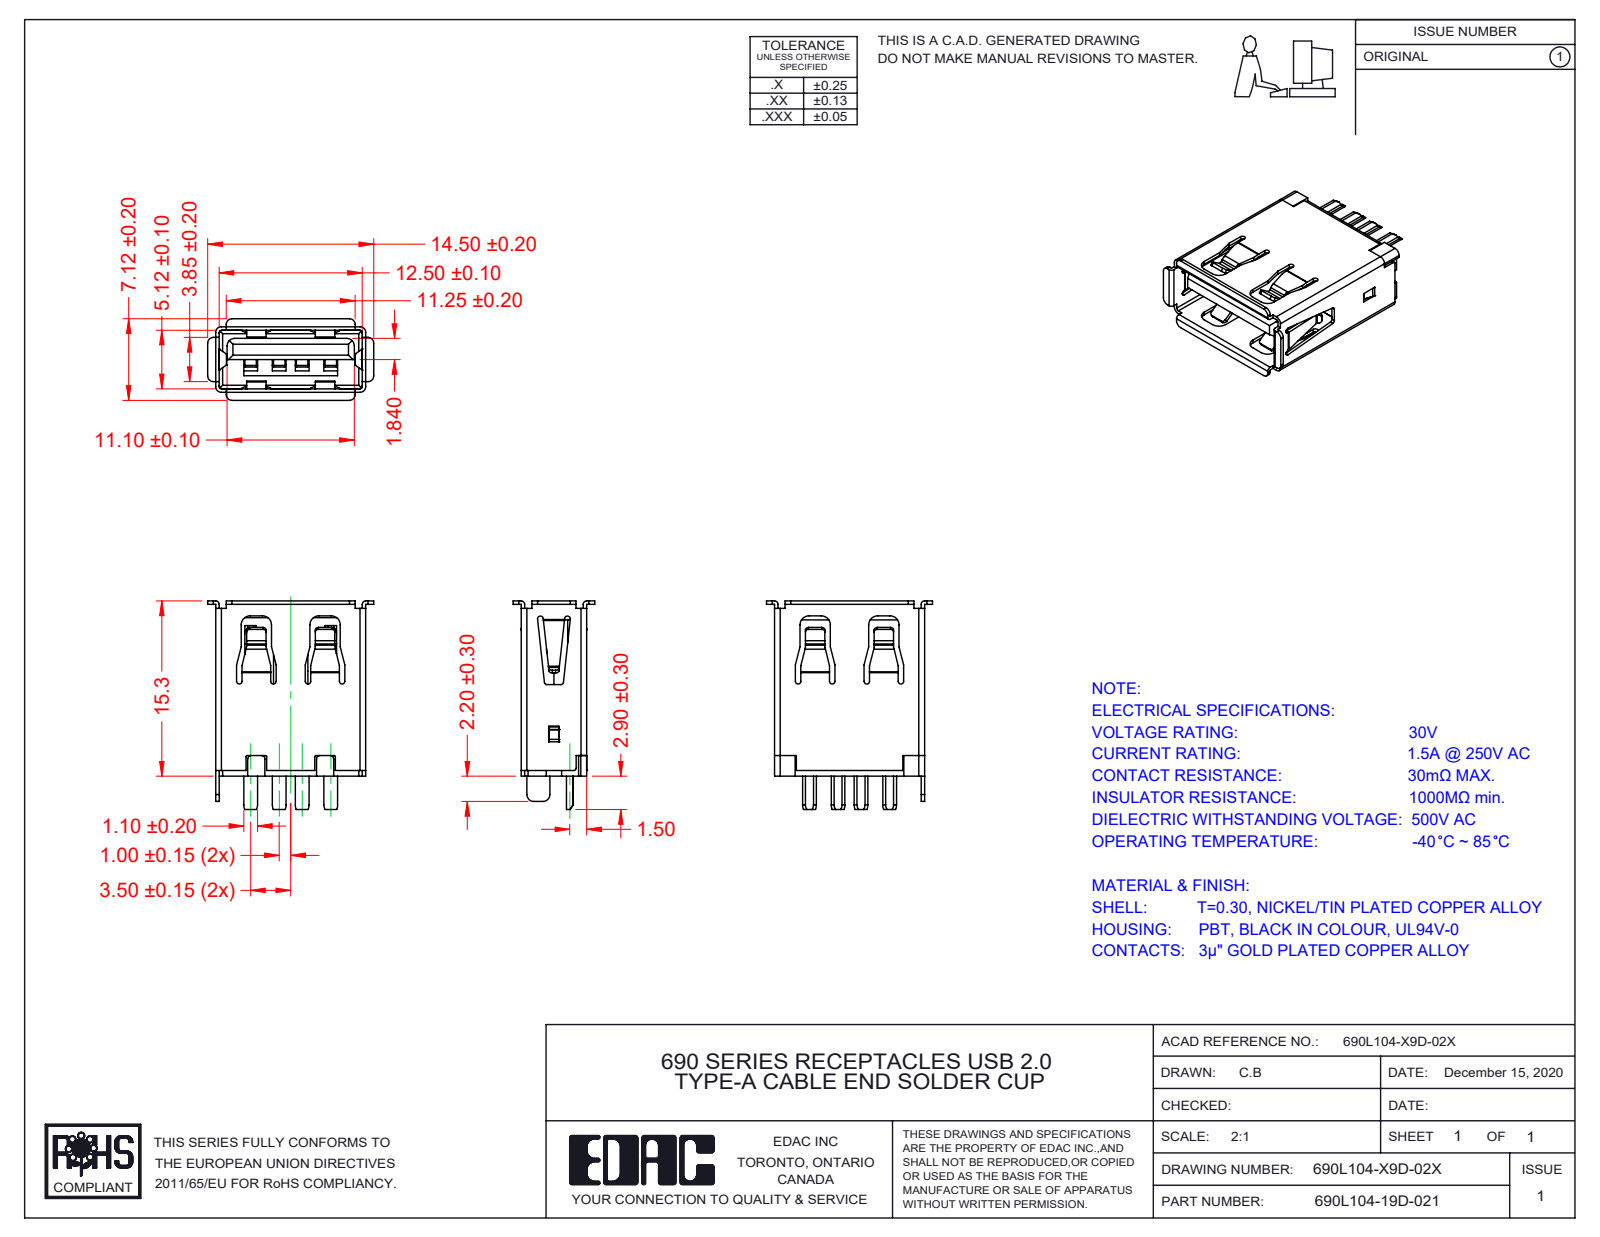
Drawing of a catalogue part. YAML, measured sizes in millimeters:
part_name: "690L104-19D-021; Shell 690L104-X9D-02X; Insulator 690L104-X9D-02X_Black; Insulator 2 690L104-X9D-02X_Black (+1 more)"
step_written_by: "SolidWorks 2020 (AUTOMOTIVE_DESIGN)"
units: millimeters
bodies: {solids: 7, faces: 790, planar: 558, cylindrical: 184, other: 48}
overall_size: [18.2, 14.5, 7.12]
volume: 618
surface_area: 2270
partial_cylinders:
  - {radius: 0.3, count: 19}
  - {radius: 0.5, count: 19}
  - {radius: 0.1, count: 16}
  - {radius: 0.2, count: 12}
  - {radius: 0.6, count: 9}
  - {radius: 0.27, count: 8}
  - {radius: 0.25, count: 6}
  - {radius: 0.4, count: 6}
face_to_face_distances: [5.42, 2.55, 5.12, 5.72, 5.41, 0.31, 5.11, 2.86, 2.56, 12.8]
